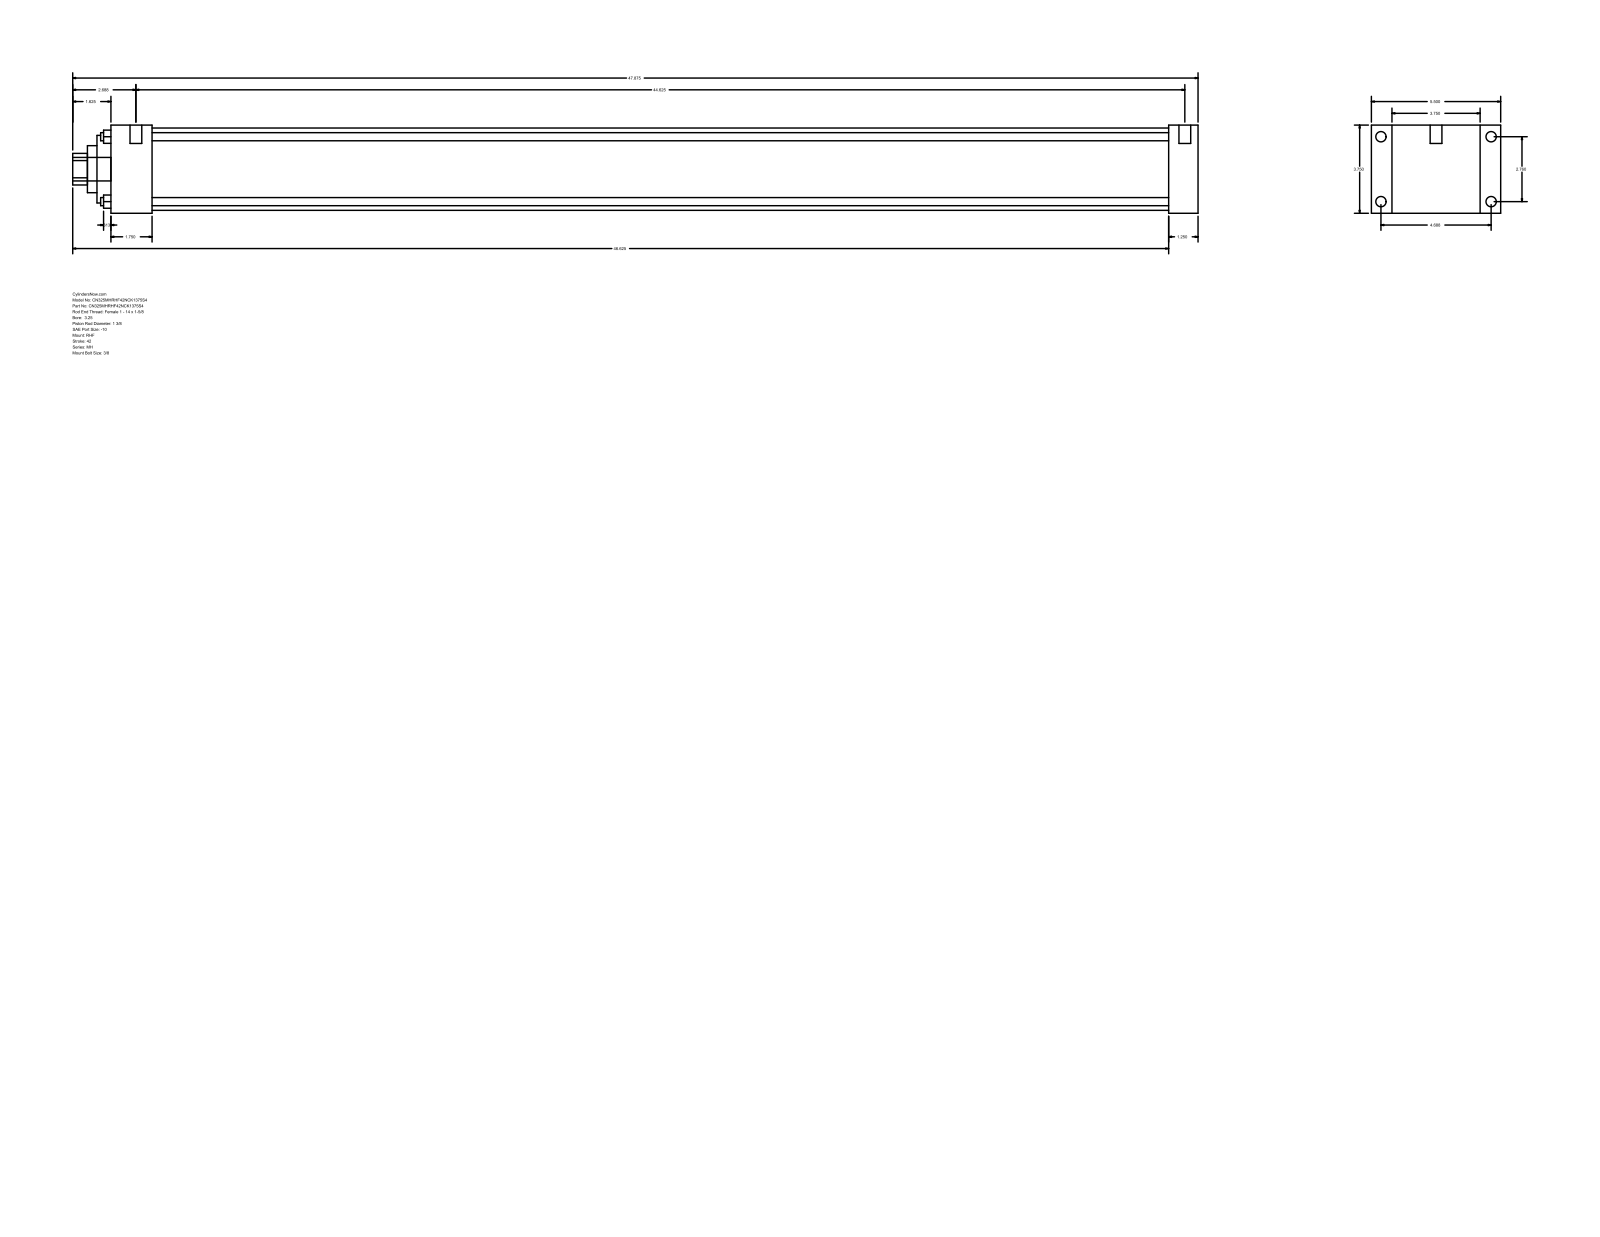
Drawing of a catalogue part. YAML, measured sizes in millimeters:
part_name: "MH_RHF__0325_1.375"
step_written_by: "GSSL Pune (CONFIG_CONTROL_DESIGN)"
units: millimeters
bodies: {solids: 0, faces: 90, planar: 61, cylindrical: 29, other: 0}
overall_size: [1216.03, 139.7, 95.25]
round_holes:
  - {diameter: 8.76, count: 4}
  - {diameter: 34.92, count: 1}
  - {diameter: 50.8, count: 1}
  - {diameter: 73.03, count: 1}
  - {diameter: 88.9, count: 1}
round_bosses_or_shafts:
  - {diameter: 11.13, count: 4}
  - {diameter: 5.56, count: 4}
  - {diameter: 12.7, count: 2}
  - {diameter: 25.4, count: 1}
partial_cylinders:
  - {radius: 17.06, count: 1}
face_to_face_distances: [95.24, 31.75, 22.23, 117.47, 1143.01, 1174.76, 139.7, 44.45, 1098.56, 1130.31]
hole_center_spacings: [49.57, 70.1, 99.14]
